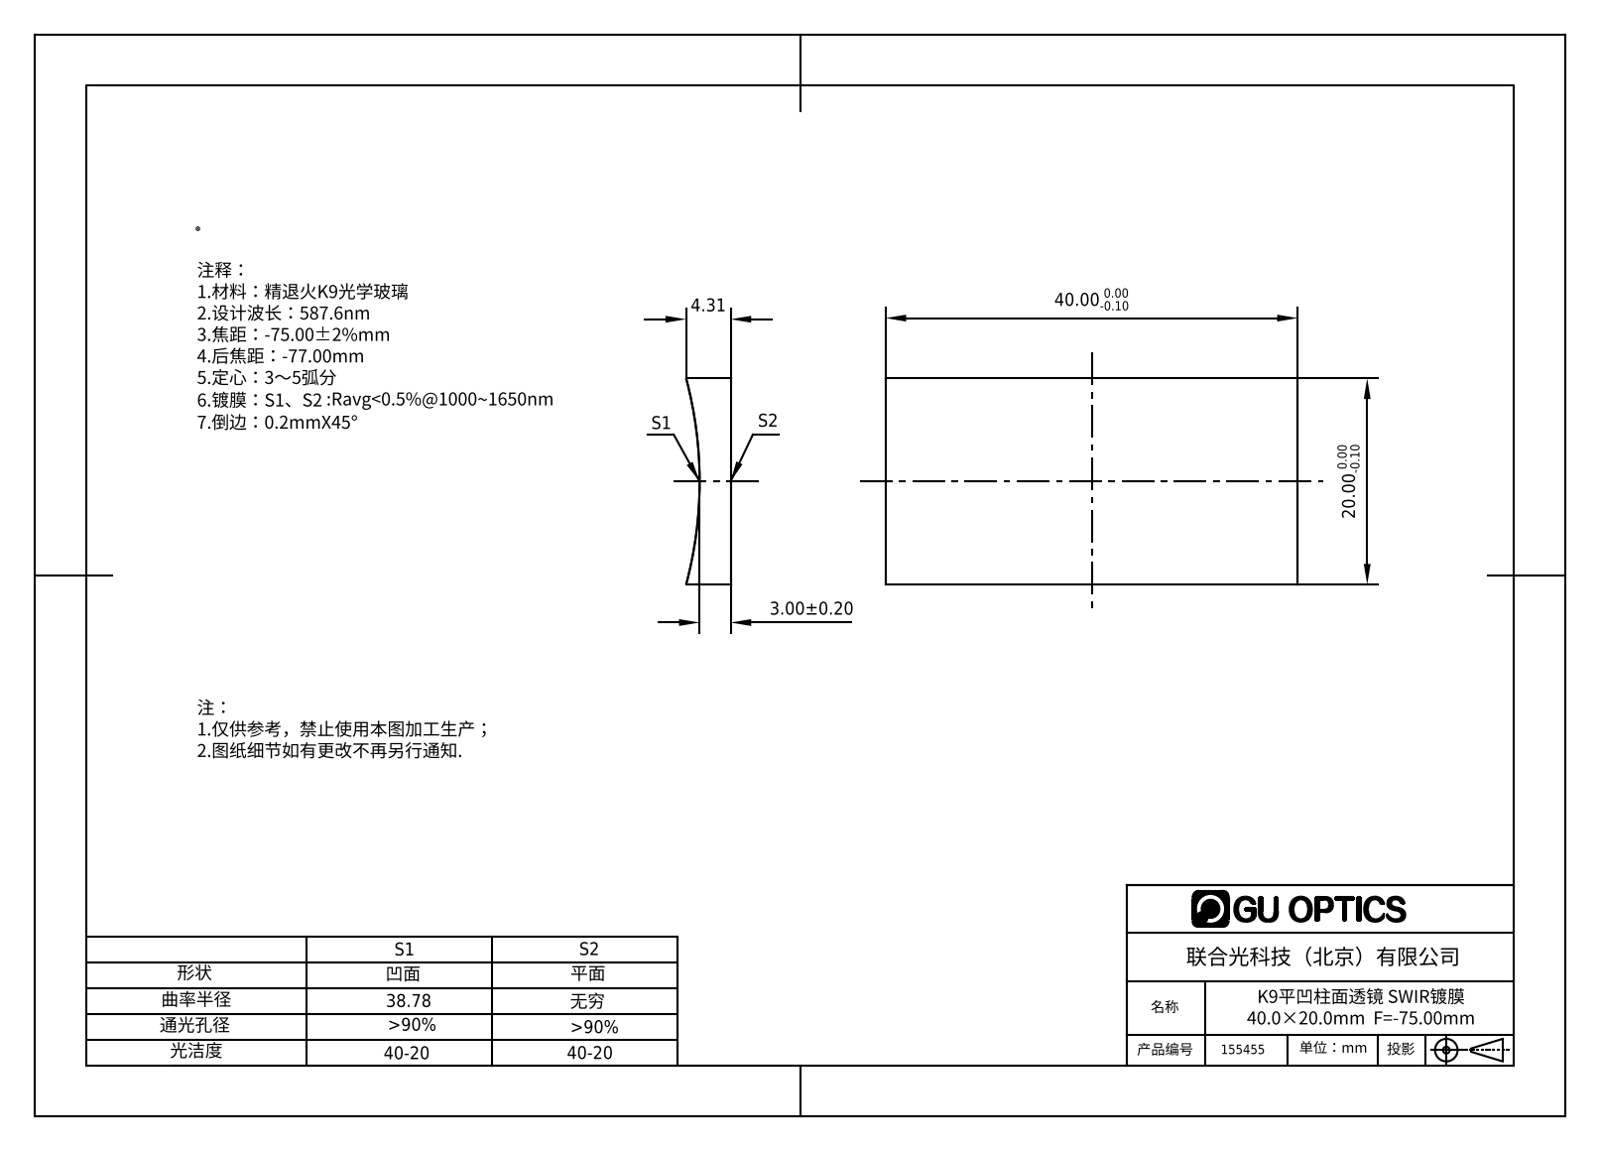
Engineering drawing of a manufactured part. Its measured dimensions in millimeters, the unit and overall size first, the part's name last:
Units: millimetres
Overall size (bounding box): 40 × 20 × 4.31
Partial cylindrical surfaces — rounded edges, fillets, slot ends (radius × count): R38.78 ×1
Main face-to-face distances: 20, 40
Volume: 2 747 mm³ · Surface area: 2 091 mm²
Bodies: 1 solid, 6 faces (5 planar, 1 cylindrical, 0 other)
Part name (STEP PRODUCT): 155356
STEP written by: SolidWorks 2016 (AUTOMOTIVE_DESIGN)
